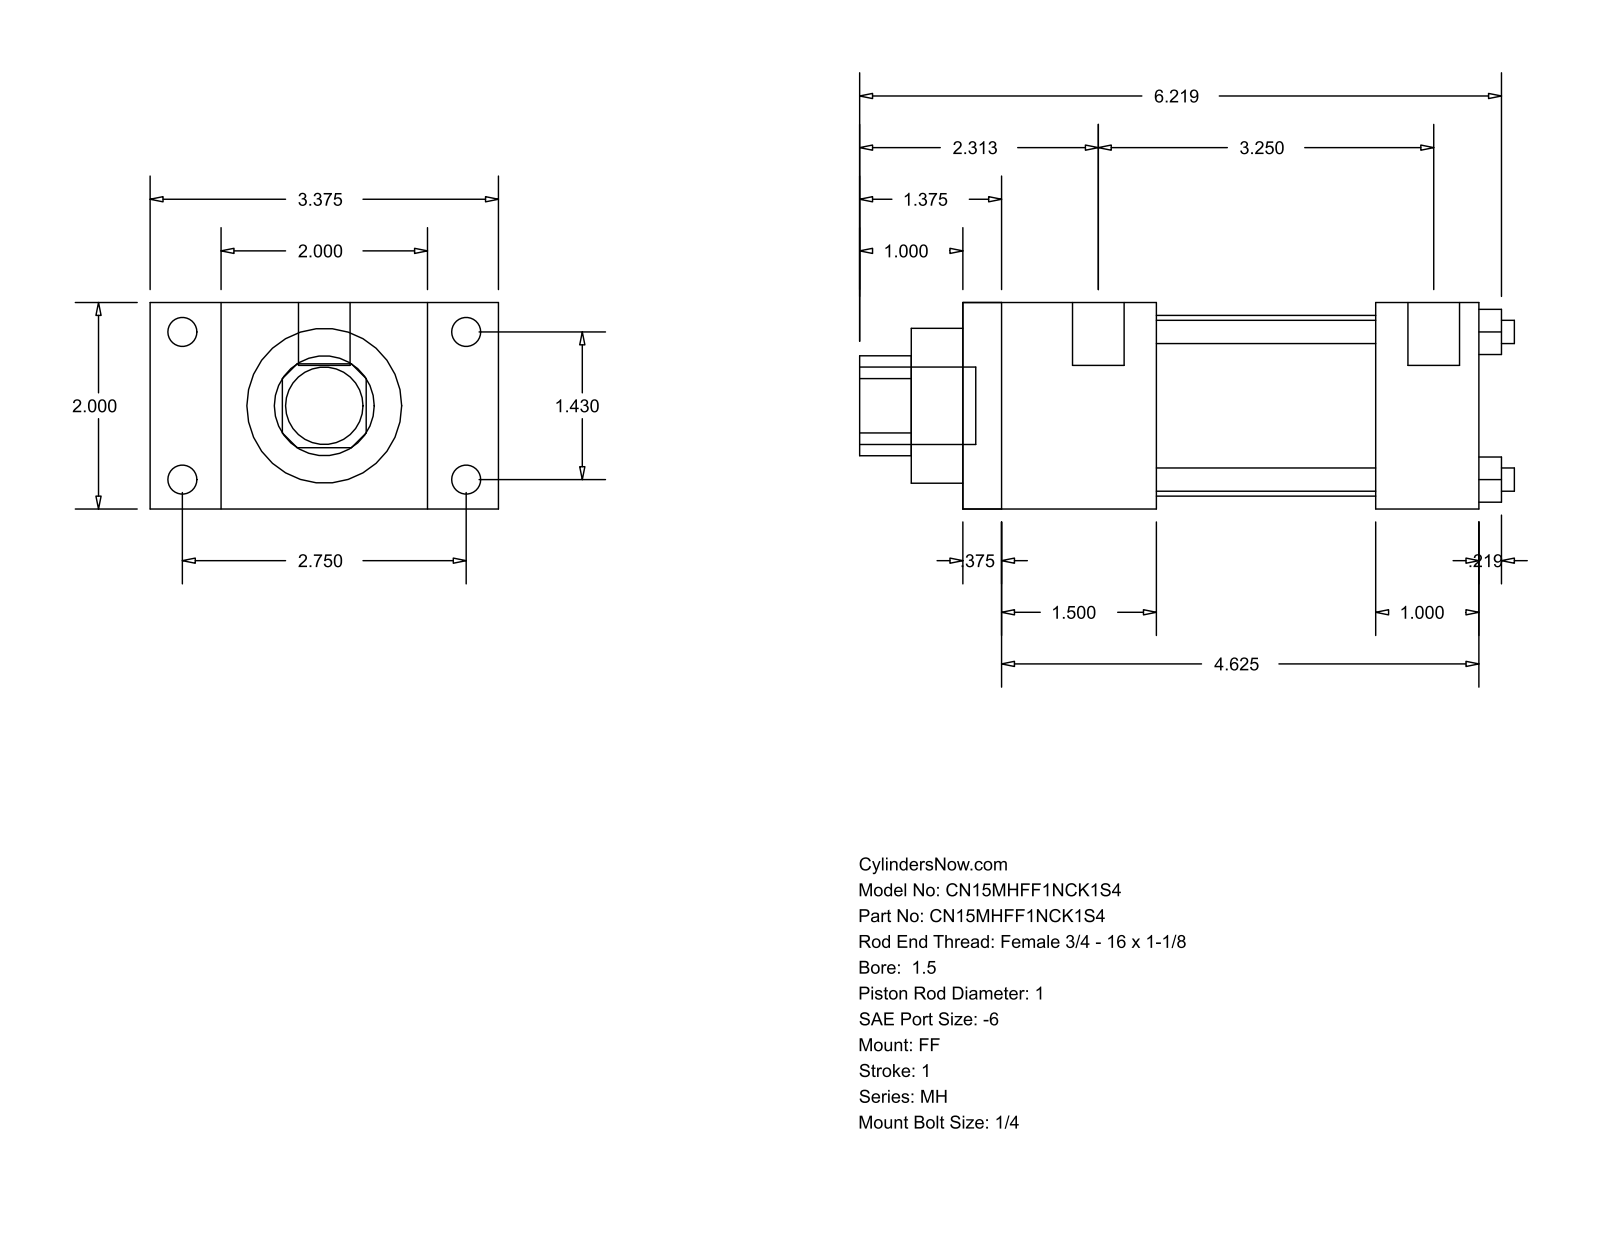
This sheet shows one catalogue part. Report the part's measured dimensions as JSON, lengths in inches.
{"part_name": "MH_FF__0150_1", "step_written_by": "GSSL Pune (CONFIG_CONTROL_DESIGN)", "units": "inches", "bodies": {"solids": 0, "faces": 92, "planar": 64, "cylindrical": 28, "other": 0}, "overall_size": [6.344, 3.375, 2], "round_holes": [[0.225, 4], [1, 1], [1.5, 1], [1.75, 1]], "round_bosses_or_shafts": [[0.281, 4], [0.219, 4], [0.5, 2], [0.75, 1]], "partial_cylinders_radius": [[0.484, 1]], "face_to_face_distances": [2, 5, 0.375, 4.625, 1, 0.687, 2.687, 1.875, 1.5, 3.125], "hole_center_spacings": [1.011, 1.43, 2.022]}
